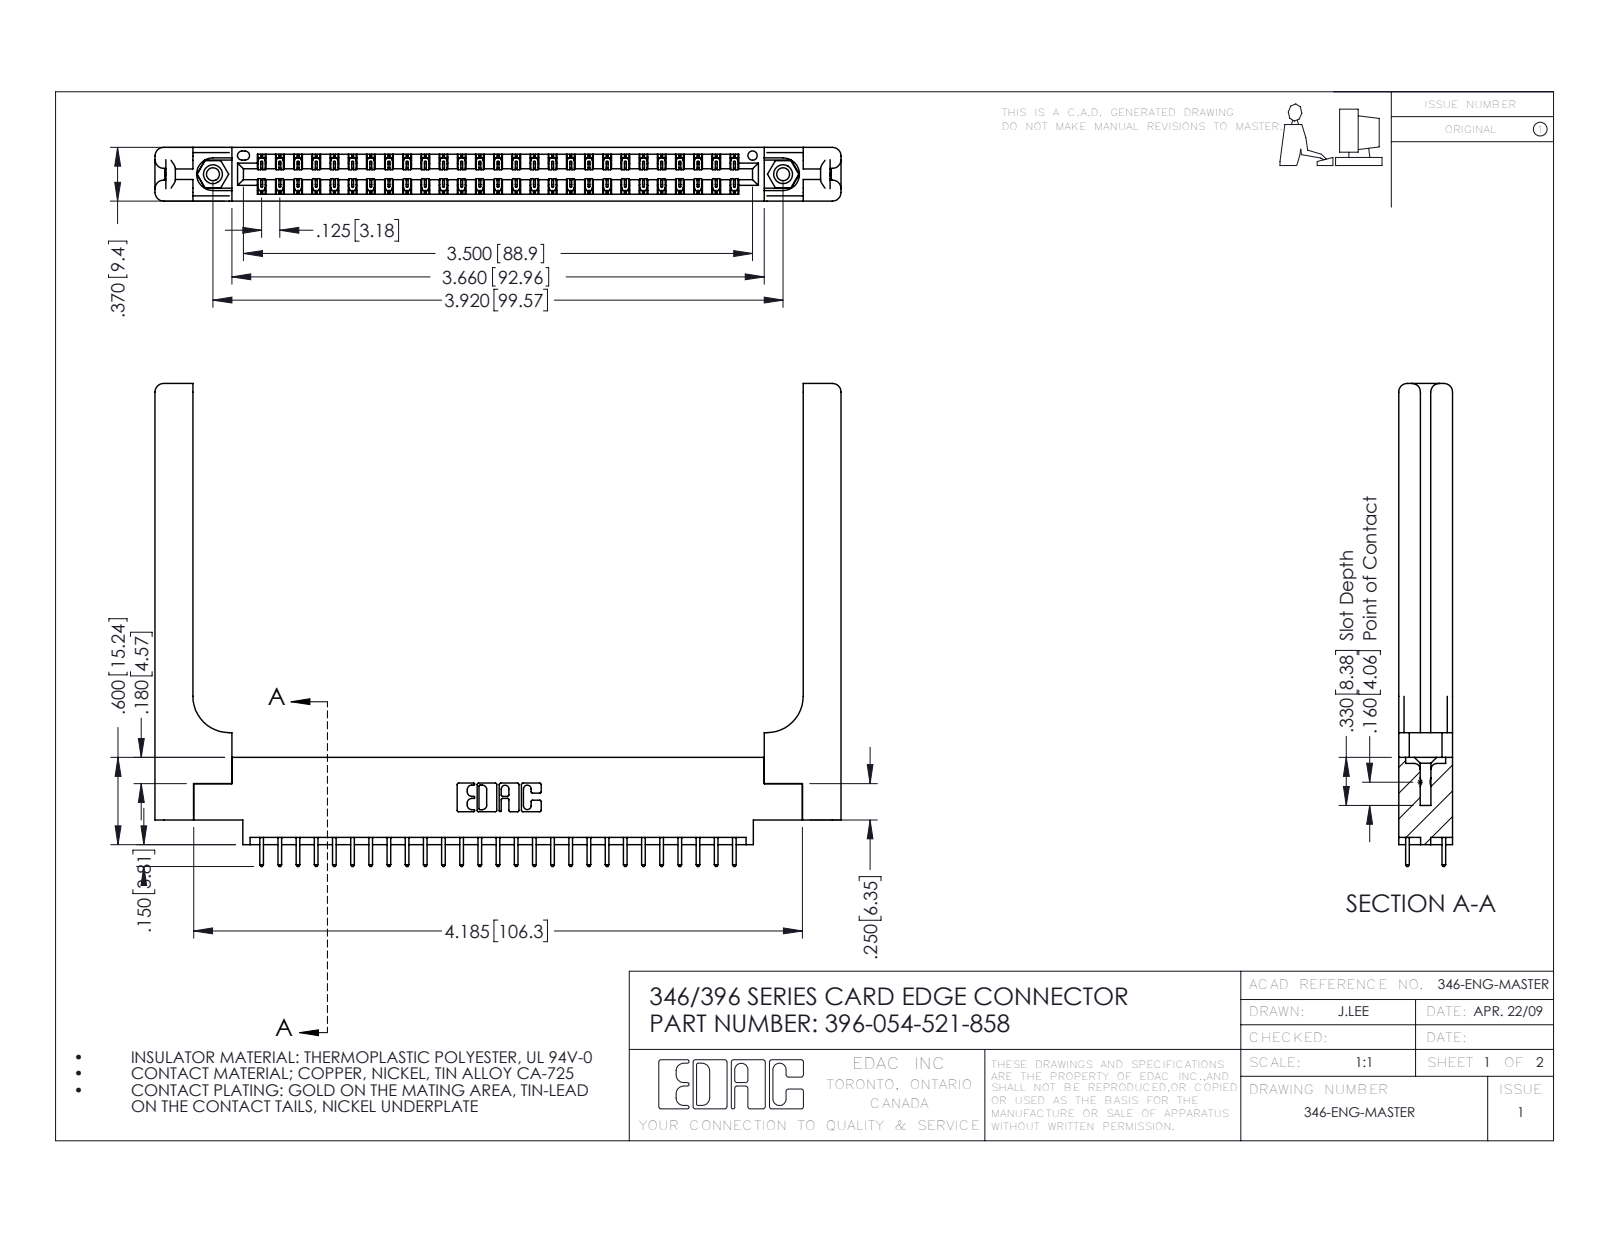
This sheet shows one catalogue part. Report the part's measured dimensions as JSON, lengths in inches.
{"part_name": "396-054-521-858; 346 Part_0.170 Offset - 0.156 Dia-TH; 345-250-001_345-250-001-102; 345-292-001_345-293-121 (+1 more)", "step_written_by": "SolidWorks 2016 (CONFIG_CONTROL_DESIGN)", "units": "inches", "bodies": {"solids": 59, "faces": 3190, "planar": 2118, "cylindrical": 1012, "other": 60}, "overall_size": [4.716, 3.32, 0.37], "volume_in3": 1.152, "surface_area_in2": 31.65, "round_holes": [[0.089, 2], [0.125, 2], [0.156, 2], [0.064, 1]], "round_bosses_or_shafts": [[0.155, 2]], "partial_cylinders_radius": [[0.006, 81], [0.01, 54], [0.01, 22], [0.06, 16], [0.007, 6], [0.031, 6], [0.026, 3], [0.014, 2]], "face_to_face_distances": [0.37, 0.072, 0.048, 0.322, 0.148, 0.15, 0.25, 0.025, 0.298, 0.275], "hole_center_spacings": [0.246, 3.712, 3.92]}
